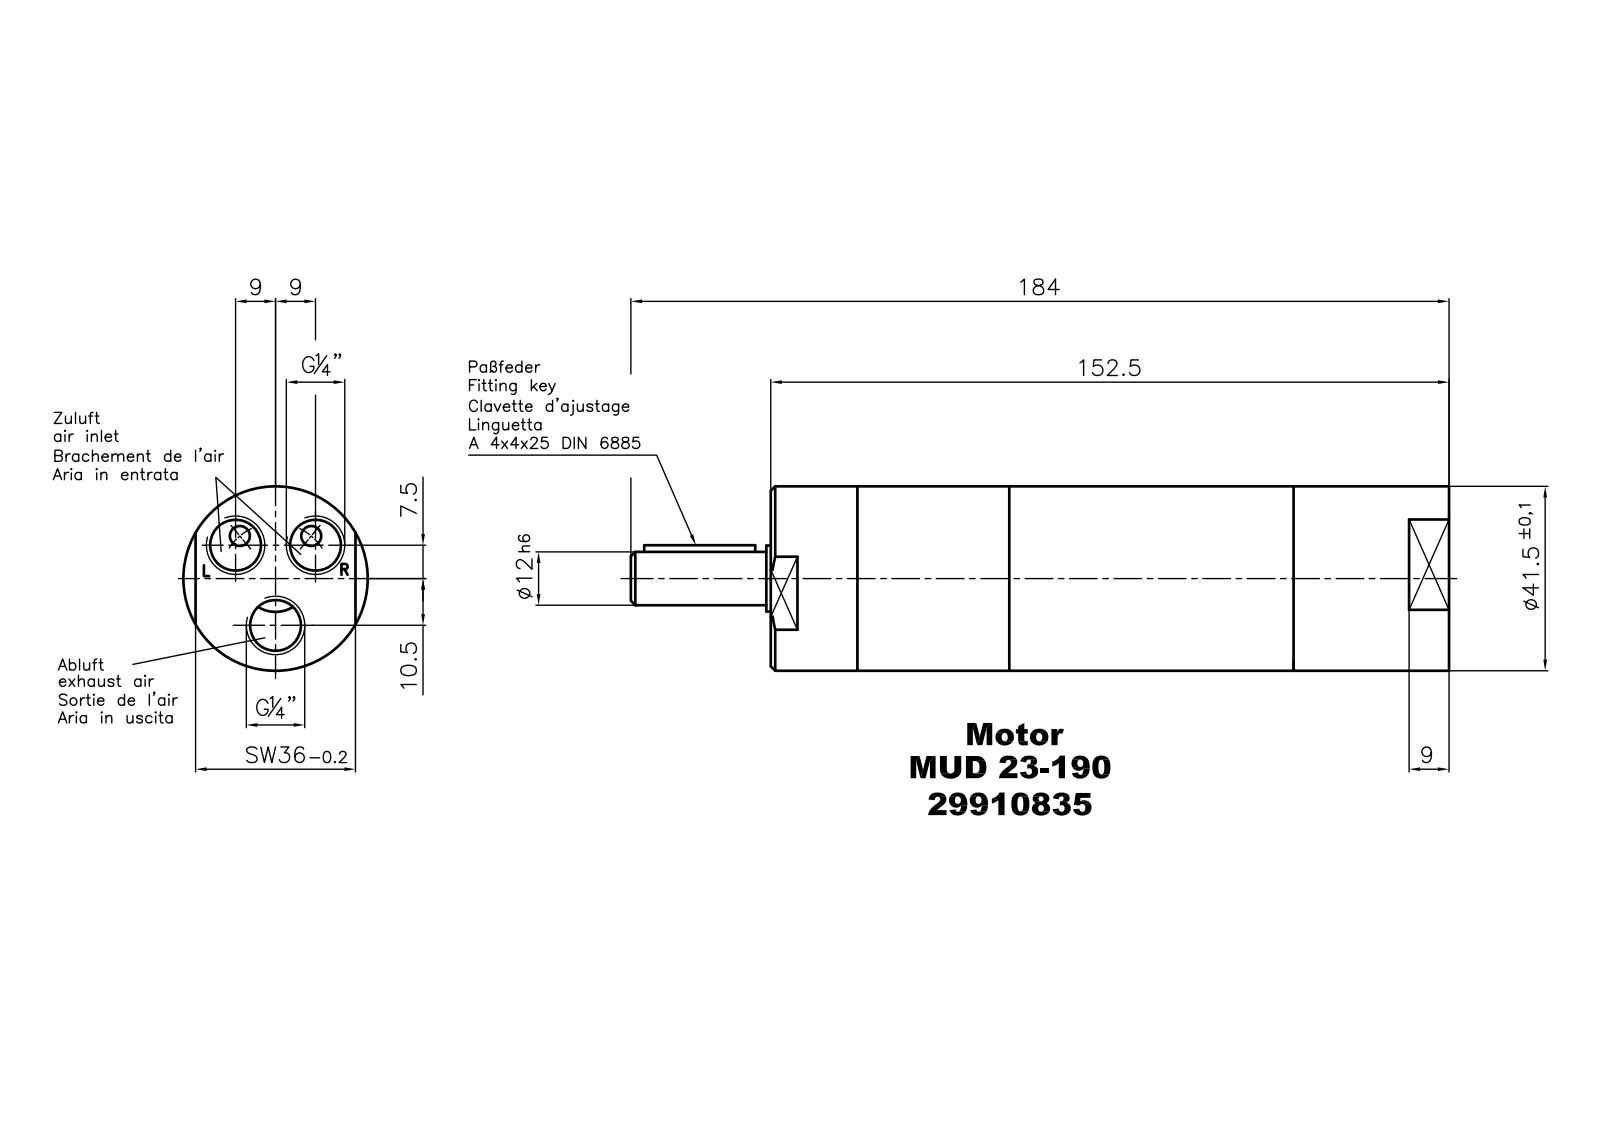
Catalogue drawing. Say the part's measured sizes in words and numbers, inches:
The part is named "MUD 23-190_29910835". Its 3-D file was written by "Autodesk Inventor 2008 (CONFIG_CONTROL_DESIGN)". It is 1 solid with 60 faces: 30 planar, 10 cylindrical and 20 other. Overall it measures 7.256 by 1.634 by 1.634 inches. Its volume is 12.4 cubic inches and its surface area 41 square inches. Round holes: 1 of diameter 0.63. Round bosses or shafts: 1 of diameter 1.634, 1 of diameter 1.474, 1 of diameter 0.589, 1 of diameter 0.472. Partial cylindrical surfaces (rounded edges, fillets, slot ends): 2 of radius 0.079. The main face-to-face distances are 6.016, 0.039, 1.457, 1.496, 4.626, 1.39, 4.638, 1.378, 1.417, 5.299.
